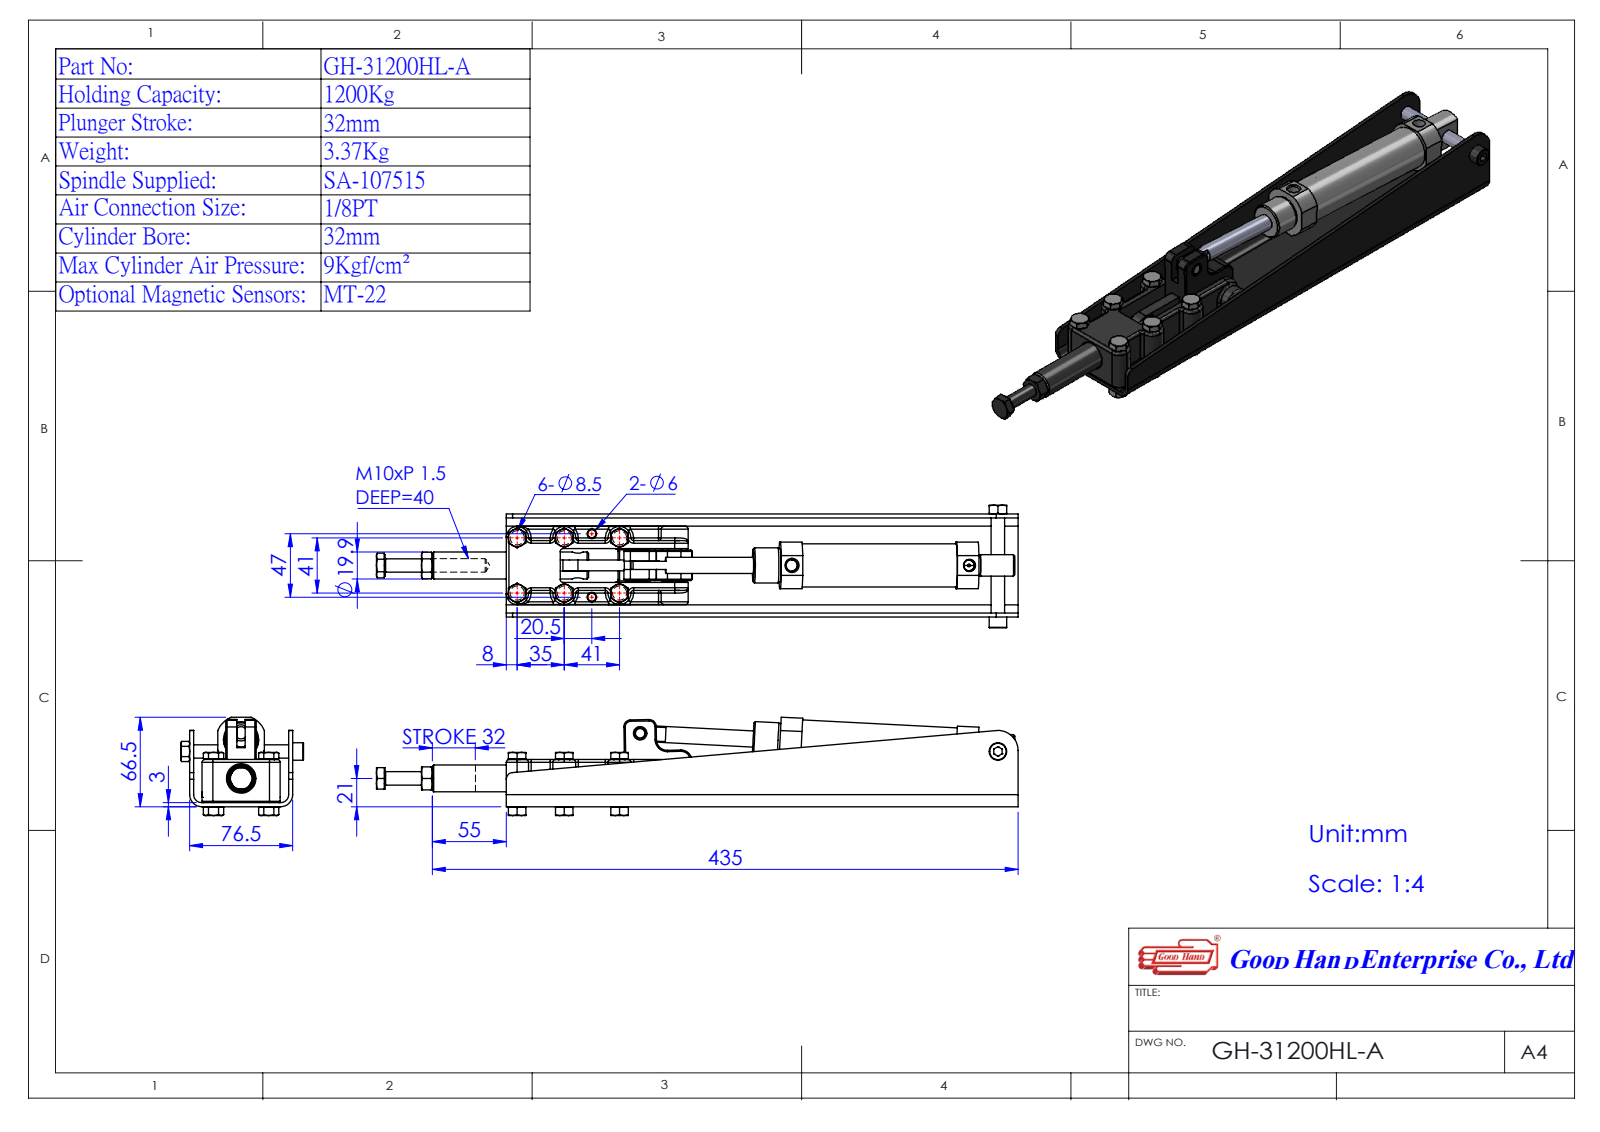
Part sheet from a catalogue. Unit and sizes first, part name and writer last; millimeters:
Units: millimetres
Overall size (bounding box): 476.4 × 88.3 × 72.95
Round holes (diameter × count): ⌀6 ×6, ⌀7.9 ×2, ⌀8.5 ×2, ⌀10 ×1, ⌀12 ×1, ⌀15 ×1, ⌀19.93 ×1, ⌀30 ×1
Round bosses / shafts (diameter × count): ⌀13 ×7, ⌀32 ×1, ⌀26 ×1, ⌀25 ×1, ⌀19.92 ×1, ⌀16 ×1, ⌀12 ×1, ⌀10 ×1
Partial cylindrical surfaces — rounded edges, fillets, slot ends (radius × count): R2 ×32, R1 ×17, R8 ×6, R8.5 ×6, R5 ×3, R9 ×3, R6 ×2, R10 ×2
Main face-to-face distances: 3, 73.5, 70.5, 76.5, 22.75, 25.75, 50.75, 47.75, 7.2, 6
Hole centre spacings: 26, 34.01, 42.2, 46.01, 47, 57.18, 72, 90.11
Volume: 468 064 mm³ · Surface area: 213 022 mm²
Bodies: 7 solids, 757 faces (285 planar, 191 cylindrical, 281 other)
Part name (STEP PRODUCT): Group3^GH-31200HL-A(簡化); Group1^GH-31200HL-A(簡化); SDA serial cylinder A_SDA 32×75-1^GH-31200HL-A(簡化); Group4^GH-31200HL-A(簡化) (+4 more)
STEP written by: SolidWorks 2016 (AUTOMOTIVE_DESIGN)
